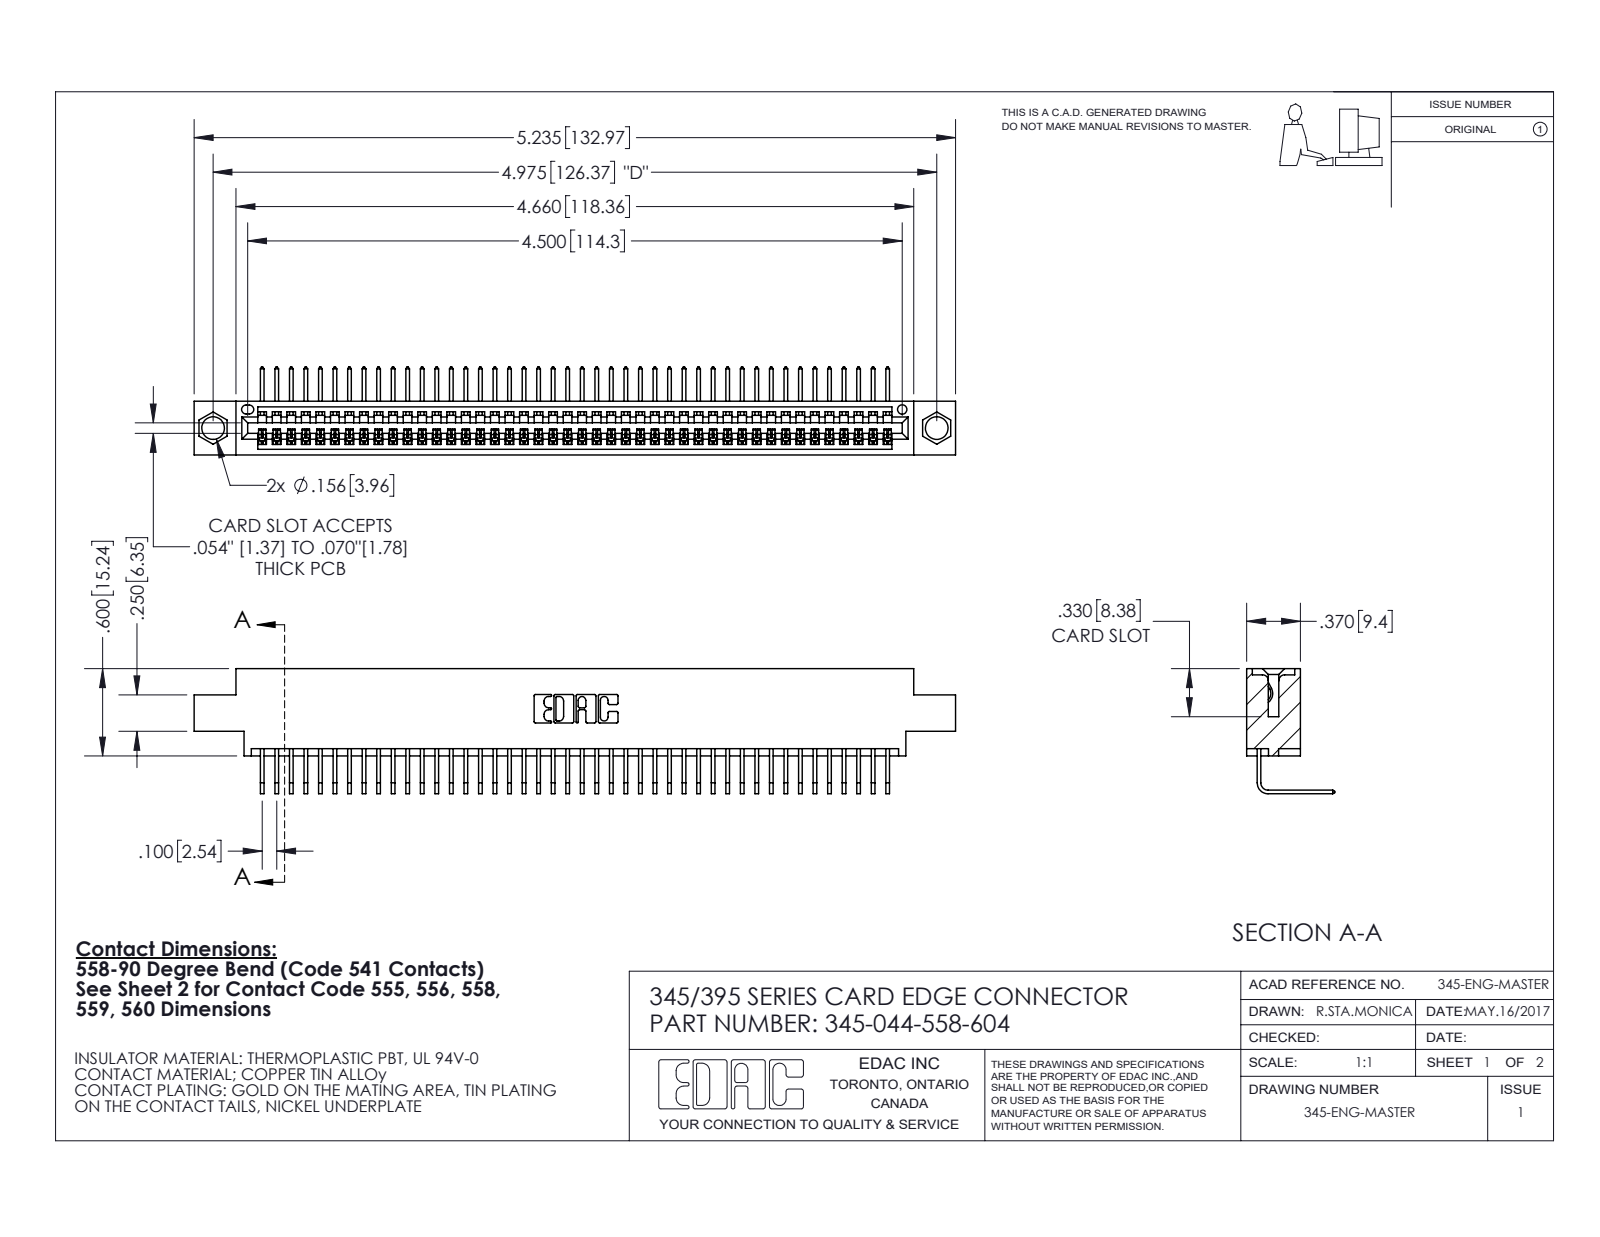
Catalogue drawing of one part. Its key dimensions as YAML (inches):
part_name: "345-044-558-604; 345-292-001_558 Tail - 2; 345 Part_0.170 Offset - 0.156 Dia-TI"
step_written_by: "SolidWorks 2020 (CONFIG_CONTROL_DESIGN)"
units: inches
bodies: {solids: 45, faces: 2784, planar: 1946, cylindrical: 838, other: 0}
overall_size: [5.235, 0.859, 0.605]
volume: 0.767
surface_area: 27.23
round_holes:
  - {diameter: 0.156, count: 2}
  - {diameter: 0.064, count: 1}
partial_cylinders:
  - {radius: 0.006, count: 88}
  - {radius: 0.01, count: 22}
  - {radius: 0.007, count: 6}
  - {radius: 0.031, count: 6}
  - {radius: 0.026, count: 3}
  - {radius: 0.031, count: 2}
  - {radius: 0.04, count: 2}
  - {radius: 0.014, count: 1}
face_to_face_distances: [0.072, 0.298, 0.37, 0.2, 0.098, 0.272, 0.025, 0.225, 0.175, 0.149]
hole_center_spacings: [0.27, 4.739, 4.975]
